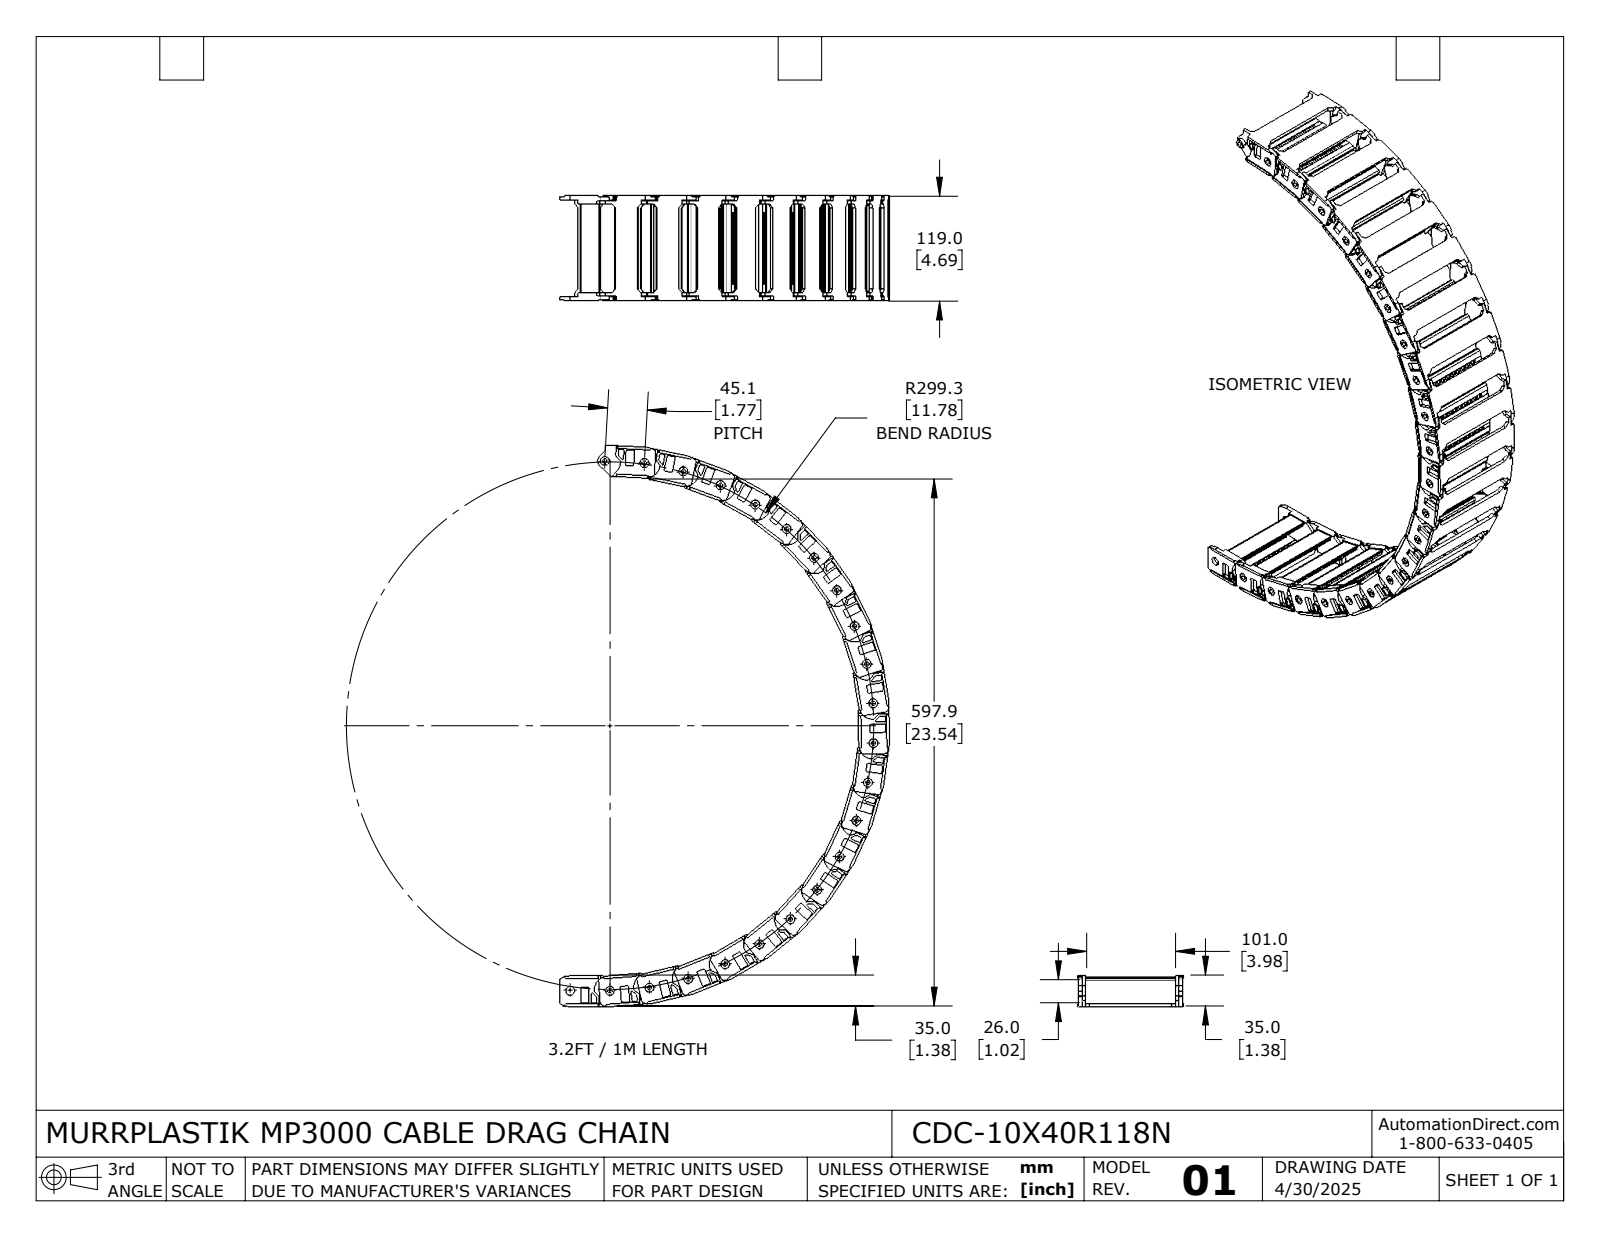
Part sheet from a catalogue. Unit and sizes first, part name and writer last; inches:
Units: inches
Overall size (bounding box): 25.009 × 14.728 × 4.685
Round holes (diameter × count): ⌀0.201 ×22, ⌀0.398 ×22
Round bosses / shafts (diameter × count): ⌀0.394 ×22
Partial cylindrical surfaces — rounded edges, fillets, slot ends (radius × count): R0.039 ×176, R0.02 ×88, R0.059 ×44, R0.079 ×44, R0.827 ×44, R0.11 ×22, R0.315 ×22, R0.709 ×22
Main face-to-face distances: 4.291, 0.315, 0.157, 0.146, 4.461, 0.169, 4.146, 0.138, 3.976, 0.031
Hole centre spacings: 8.669, 1.772, 5.281, 10.294, 5.28, 6.994, 6.995, 1.774
Volume: 50.31 in³ · Surface area: 794 in²
Bodies: 22 solids, 5456 faces (4356 planar, 1100 cylindrical, 0 other)
Part name (STEP PRODUCT): CDC-10X40R118N
STEP written by: SolidWorks 2024 (AUTOMOTIVE_DESIGN)
